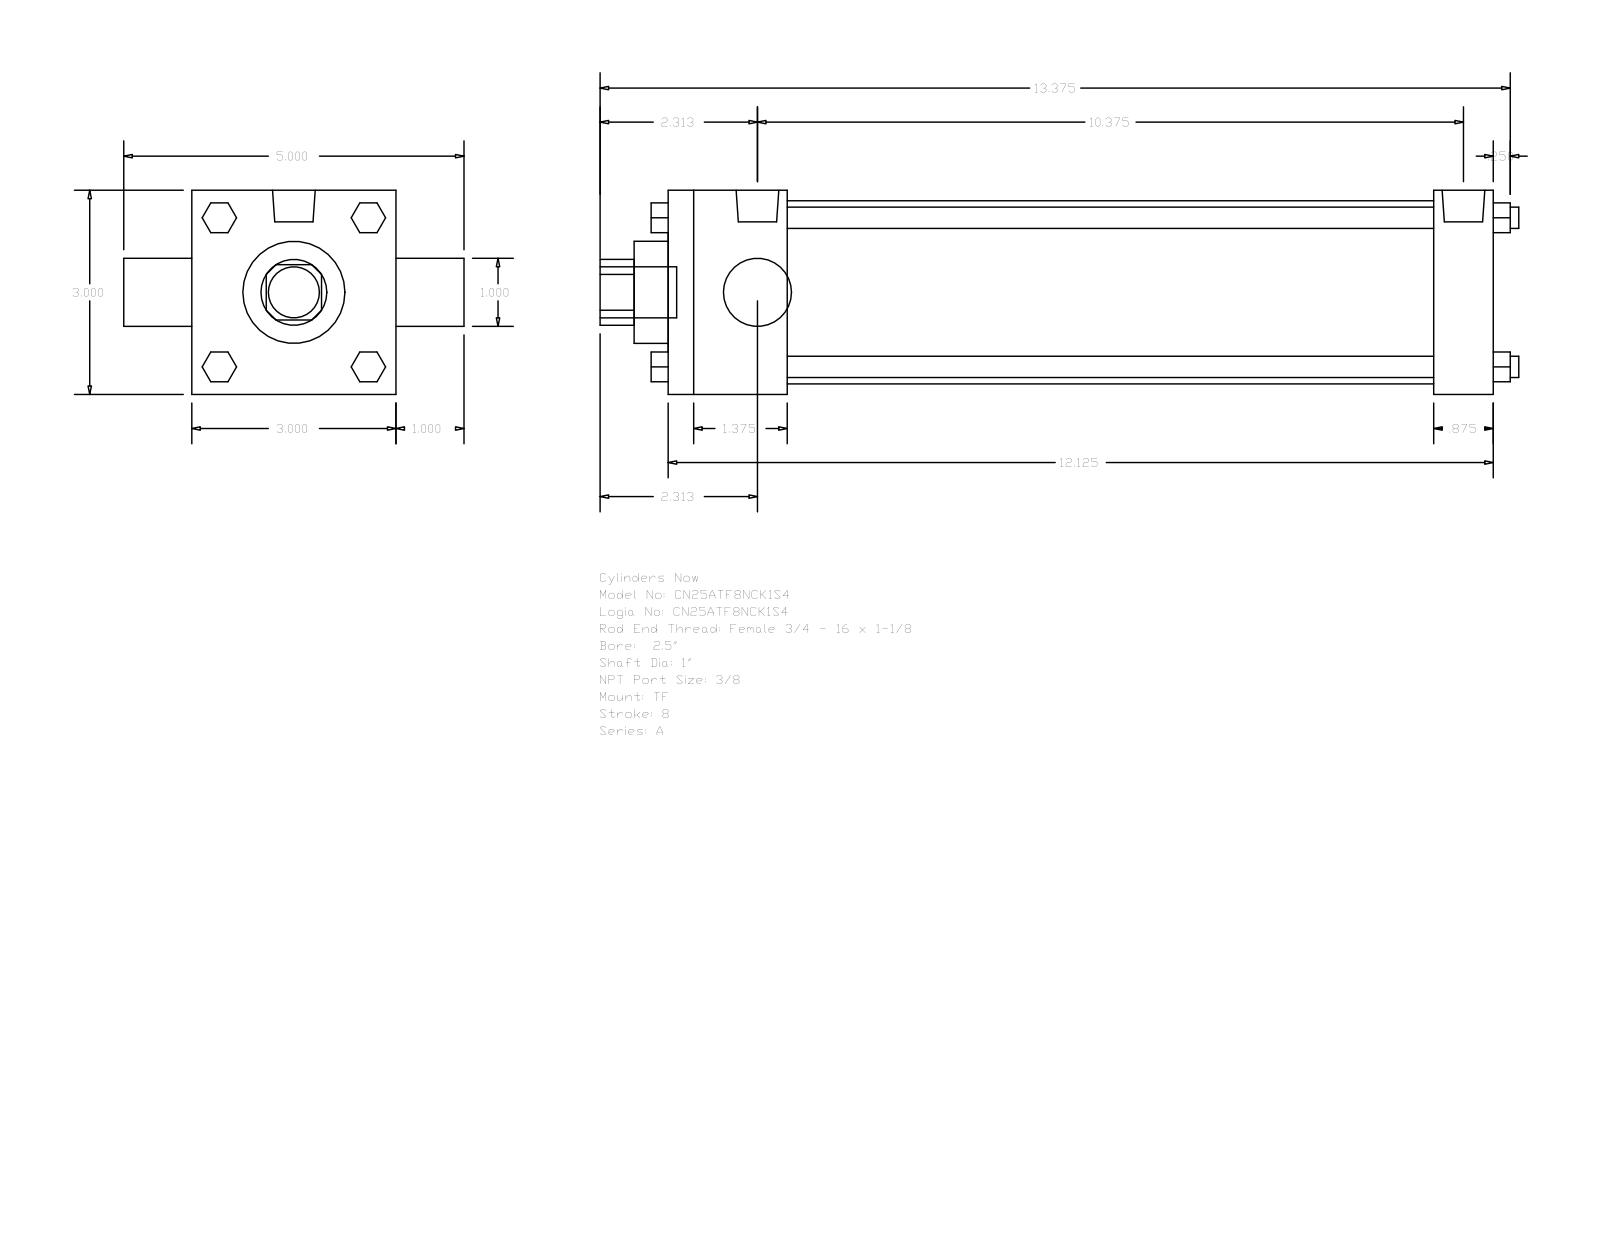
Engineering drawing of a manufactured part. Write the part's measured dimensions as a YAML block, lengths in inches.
part_name: "A_TF__0250_1"
step_written_by: "GSSL Pune (CONFIG_CONTROL_DESIGN)"
units: inches
bodies: {solids: 0, faces: 120, planar: 92, cylindrical: 28, other: 0}
overall_size: [13.5, 5, 3]
round_holes:
  - {diameter: 1, count: 2}
  - {diameter: 1.5, count: 1}
  - {diameter: 2.69, count: 1}
round_bosses_or_shafts:
  - {diameter: 0.313, count: 4}
  - {diameter: 0.219, count: 3}
  - {diameter: 0.627, count: 2}
  - {diameter: 0.75, count: 1}
partial_cylinders:
  - {radius: 0.484, count: 1}
face_to_face_distances: [3, 12.125, 1.75, 11.25, 9.5, 10.375, 0.875, 1, 4, 12.625]
